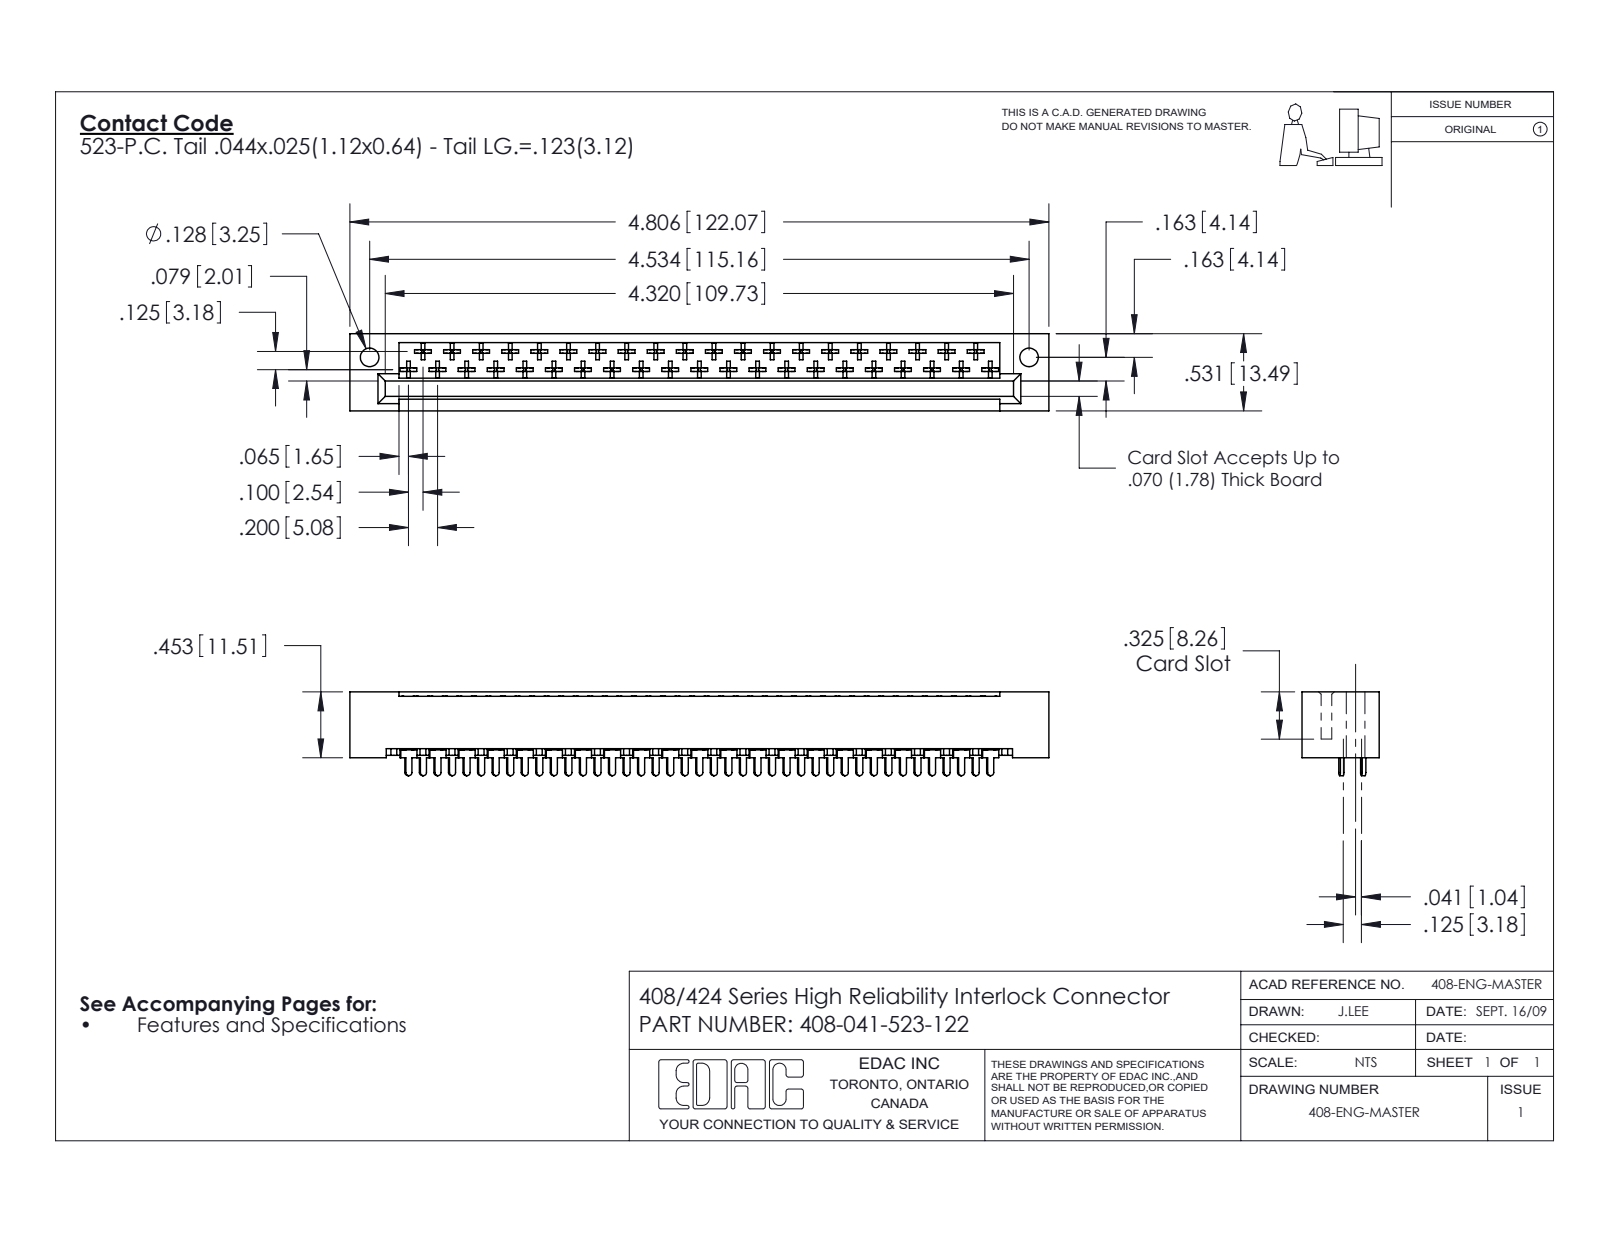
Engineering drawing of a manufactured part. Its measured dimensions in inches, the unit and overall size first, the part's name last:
Units: inches
Overall size (bounding box): 4.806 × 0.576 × 0.531
Round holes (diameter × count): ⌀0.128 ×2
Partial cylindrical surfaces — rounded edges, fillets, slot ends (radius × count): R0.01 ×246, R0.02 ×43, R0.022 ×41
Main face-to-face distances: 0.1, 0.296, 0.531, 0.125, 0.025, 0.025, 0.259, 0.272, 0.235, 0.135
Hole centre spacings: 4.534
Volume: 0.809 in³ · Surface area: 25.77 in²
Bodies: 42 solids, 2299 faces (1758 planar, 377 cylindrical, 164 other)
Part name (STEP PRODUCT): 408 Part_041 - 1; 408-290-001_408-290-123 - Top; 408-290-001_408-290-123 - Bottom; 408-047-523-122
STEP written by: SolidWorks 2016 (CONFIG_CONTROL_DESIGN)
